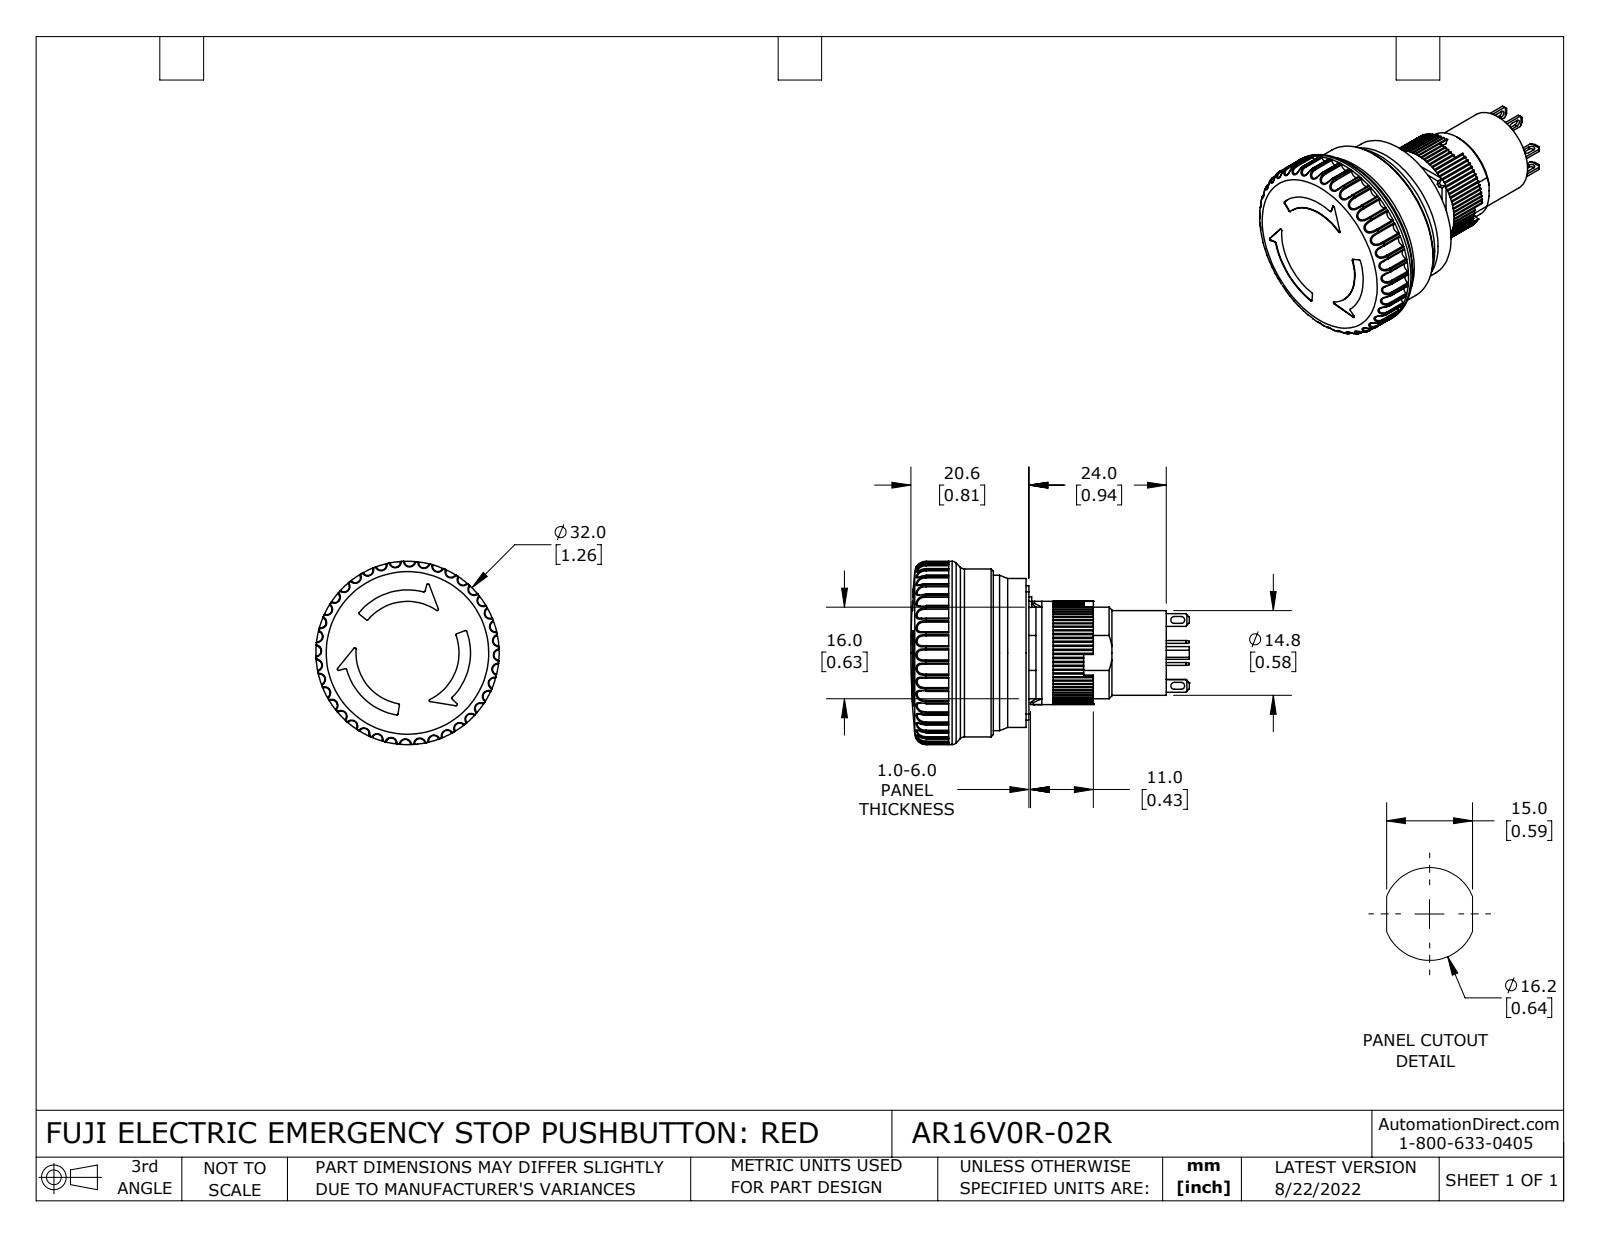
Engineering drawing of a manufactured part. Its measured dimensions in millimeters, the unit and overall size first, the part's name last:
Units: millimetres
Overall size (bounding box): 48.6 × 32 × 32
Round holes (diameter × count): ⌀14.8 ×1, ⌀16 ×1, ⌀27.2 ×1
Round bosses / shafts (diameter × count): ⌀32 ×1, ⌀29.3 ×1, ⌀26 ×1, ⌀21.8 ×1, ⌀18 ×1, ⌀6 ×1
Partial cylindrical surfaces — rounded edges, fillets, slot ends (radius × count): R0.2 ×80, R0.3 ×80, R0.9 ×40, R0.5 ×8, R0.6 ×8, R1 ×2, R0.8 ×1, R2.9 ×1
Main face-to-face distances: 10.7, 13.5, 2.7, 1, 0.5, 1.8, 21.7, 12.4, 2.3, 1.2
Volume: 18 400 mm³ · Surface area: 8 742 mm²
Bodies: 5 solids, 921 faces (488 planar, 359 cylindrical, 74 other)
Part name (STEP PRODUCT): AR16V0R-02R
STEP written by: SolidWorks 2021 (CONFIG_CONTROL_DESIGN)
